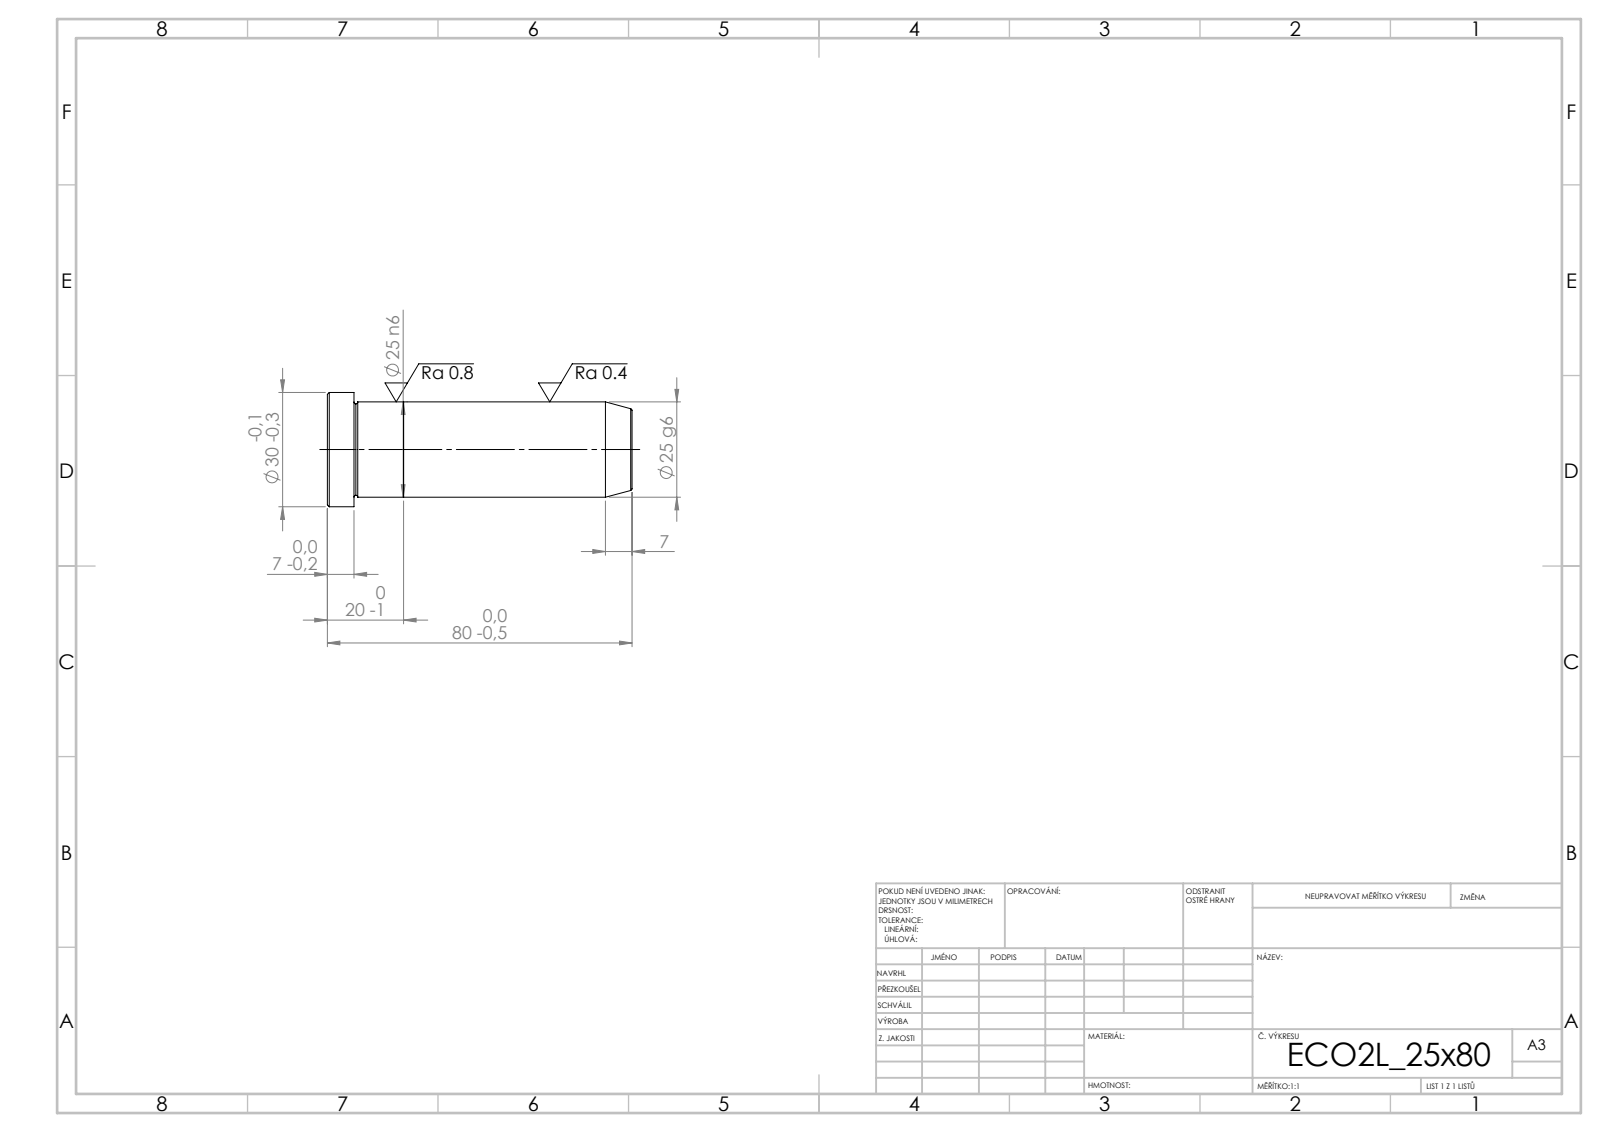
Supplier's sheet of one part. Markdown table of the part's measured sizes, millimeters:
| quantity | value |
| --- | --- |
| STEP written by | SolidWorks 2019 (CONFIG_CONTROL_DESIGN) |
| units | millimeters |
| bodies | 2 solids, 21 faces (5 planar, 6 cylindrical, 10 other) |
| overall size | 80 × 30 × 30 |
| volume | 40 248 mm³ |
| surface area | 8 635 mm² |
| round bosses / shafts (diameter × count) | 30 × 1, 25 × 1 |
| main face-to-face distances | 20, 60, 80, 73, 13, 7 |
